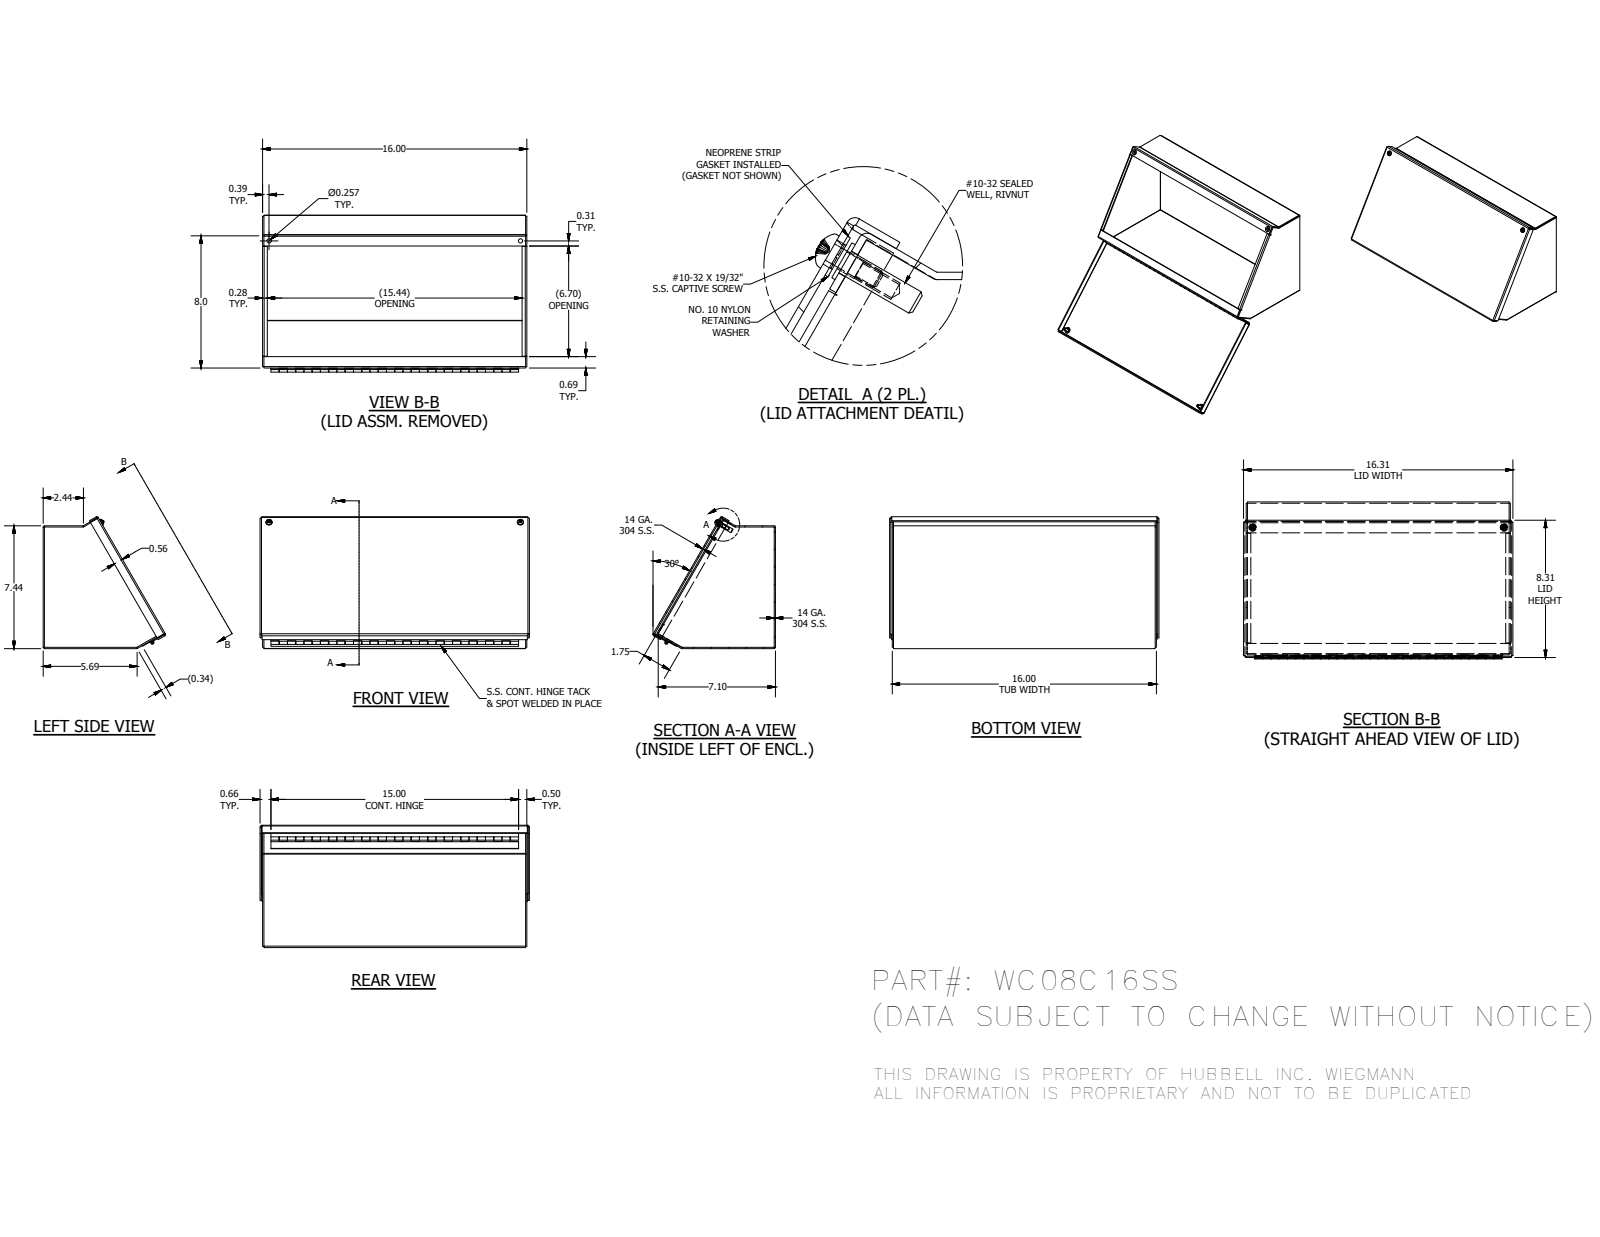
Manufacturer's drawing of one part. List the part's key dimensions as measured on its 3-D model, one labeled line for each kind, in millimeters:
Part name (STEP PRODUCT): WC08C16SSBTB; WC08C16SSLID; WC08CSSLS; WC08CSSRS (+8 more)
STEP written by: Autodesk Inventor 2014 (AUTOMOTIVE_DESIGN)
Units: millimetres
Bodies: 13 solids, 447 faces (282 planar, 113 cylindrical, 52 other)
Overall size (bounding box): 414.34 × 202.88 × 188.29
Volume: 679 939 mm³ · Surface area: 750 729 mm²
Round holes (diameter × count): ⌀3.96 ×2, ⌀4.98 ×2, ⌀6.53 ×2, ⌀7.06 ×2, ⌀7.14 ×2, ⌀2.96 ×1
Round bosses / shafts (diameter × count): ⌀11.51 ×2, ⌀10.31 ×2, ⌀9.47 ×2, ⌀6.3 ×2, ⌀4.83 ×2, ⌀5.08 ×1, ⌀2.54 ×1
Partial cylindrical surfaces — rounded edges, fillets, slot ends (radius × count): R0.4 ×12, R2.28 ×12, R2.27 ×2
Main face-to-face distances: 1.88, 404.52, 187.03, 402.64, 406.4, 185.15, 188.91, 4.26, 1.89, 203.1
Hole centre spacings: 386.74
